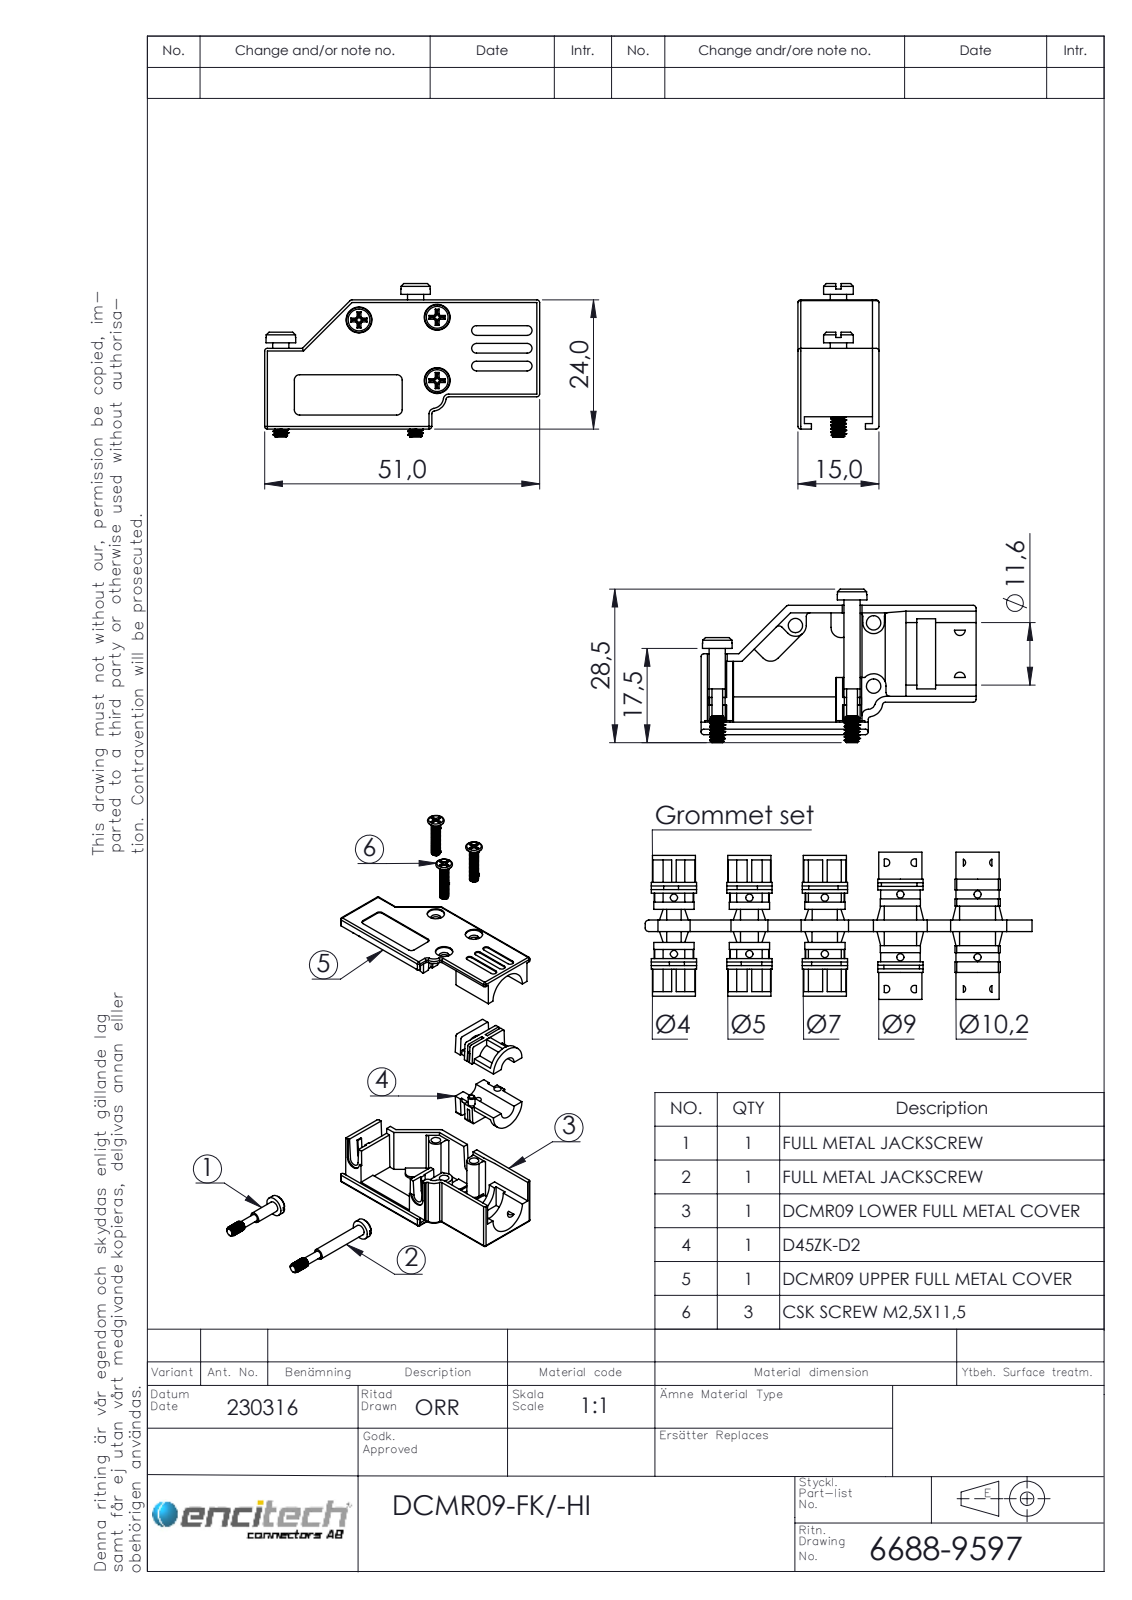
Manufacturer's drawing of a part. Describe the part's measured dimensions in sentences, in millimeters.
The part is named "6826-0128-11; 6805-0501-11; 6855-0115-03; 6805-0501-01 (+3 more)". Its 3-D file was written by "SolidWorks 2021 (AUTOMOTIVE_DESIGN)". It is 9 solids with 756 faces: 317 planar, 347 cylindrical and 92 other. Overall it measures 51 by 28.5 by 15.05 millimeters. Its volume is 7 812 cubic millimeters and its surface area 11 229 square millimeters. Round holes: 3 of diameter 2, 3 of diameter 2.65, 3 of diameter 2.8, 3 of diameter 4.8, 2 of diameter 3, 1 of diameter 5, 1 of diameter 11.6. Round bosses or shafts: 3 of diameter 2.5, 2 of diameter 5.5, 2 of diameter 2.84, 2 of diameter 2, 2 of diameter 1.9, 1 of diameter 11.2. Partial cylindrical surfaces (rounded edges, fillets, slot ends): 35 of radius 0.5, 6 of radius 0.9, 6 of radius 1, 5 of radius 0.7, 4 of radius 0.25, 4 of radius 5.91, 2 of radius 1.2, 2 of radius 1.9. The main face-to-face distances are 13, 15, 1.2, 7.5, 13.8, 2, 1.4, 6.3, 7.2, 0.8. The hole center spacings are 5.77, 9.21, 9.37, 9.92, 9.94, 10.2, 11.75, 14.51.
